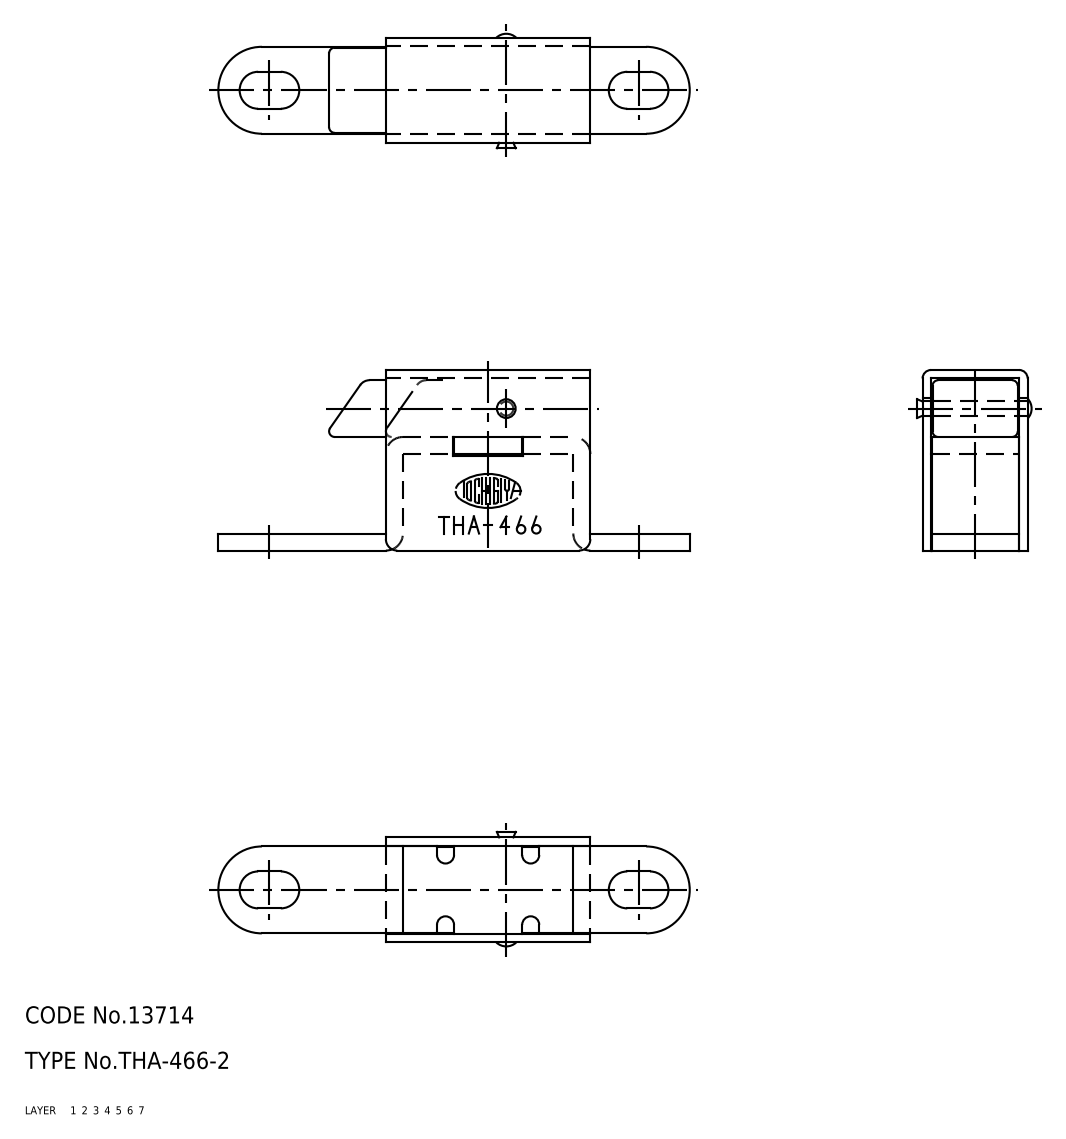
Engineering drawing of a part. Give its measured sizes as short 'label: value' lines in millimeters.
name: X2_30D930FC30B9_X0; THA_466_2; X2_30E930C330C1_X0
written by: SolidWorks 2015 (AUTOMOTIVE_DESIGN)
unit: mm
bodies: 2 solids, 118 faces (60 planar, 46 cylindrical, 12 other)
size: 83 × 31.8 × 20.15
volume: 13 187 mm³; area: 12 328 mm²
holes: 1× ⌀2.55
bosses: 1× ⌀2.5
rounds: 13× R1, 6× R1.5, 4× R3.25, 3× R2, 2× R1.35, 2× R3, 2× R4, 2× R7.65
face distances: 17, 1.5, 3, 15.5, 18.5, 20, 11.8, 31.8, 30.3, 10.3
